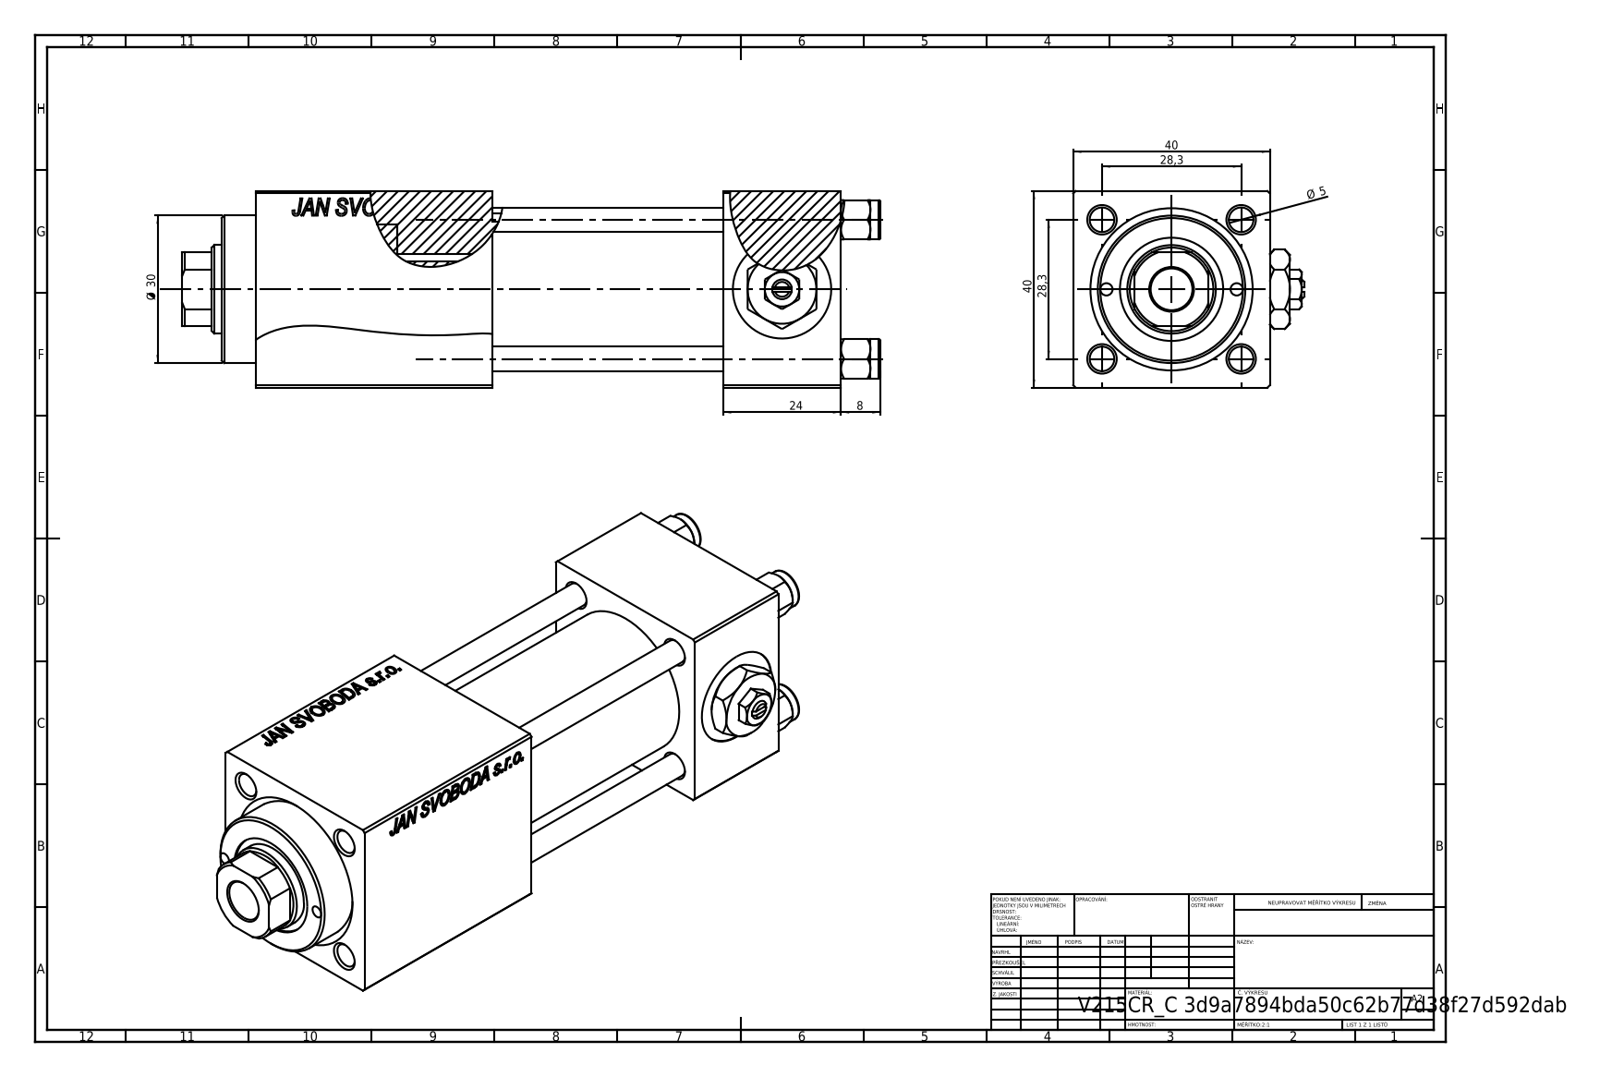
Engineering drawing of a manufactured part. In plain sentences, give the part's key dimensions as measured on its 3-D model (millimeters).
The part is named "V215CR_C_Body; NUT_M5_C; Zatka_pro_OIL_PORT; V215CR_VCP_C (+2 more)". Its 3-D file was written by "SolidWorks 2019 (CONFIG_CONTROL_DESIGN)". It is 12 solids with 1203 faces: 549 planar, 96 cylindrical and 558 other. Overall it measures 142 by 47 by 40 millimeters. Its volume is 149 125 cubic millimeters and its surface area 57 930 square millimeters. Round holes: 4 of diameter 5, 3 of diameter 20, 2 of diameter 2.5, 2 of diameter 7, 2 of diameter 13.16, 1 of diameter 8.5, 1 of diameter 18, 1 of diameter 21, 1 of diameter 25, 1 of diameter 30. Round bosses or shafts: 4 of diameter 8, 1 of diameter 31. Partial cylindrical surfaces (rounded edges, fillets, slot ends): 1 of radius 8.5. The main face-to-face distances are 40, 24, 47, 71, 90.3, 66.3, 19.3, 48, 39.8, 95. The hole center spacings are 14.18, 20.01, 28.3, 30.84, 13.25, 40.02, 26.5, 72.
